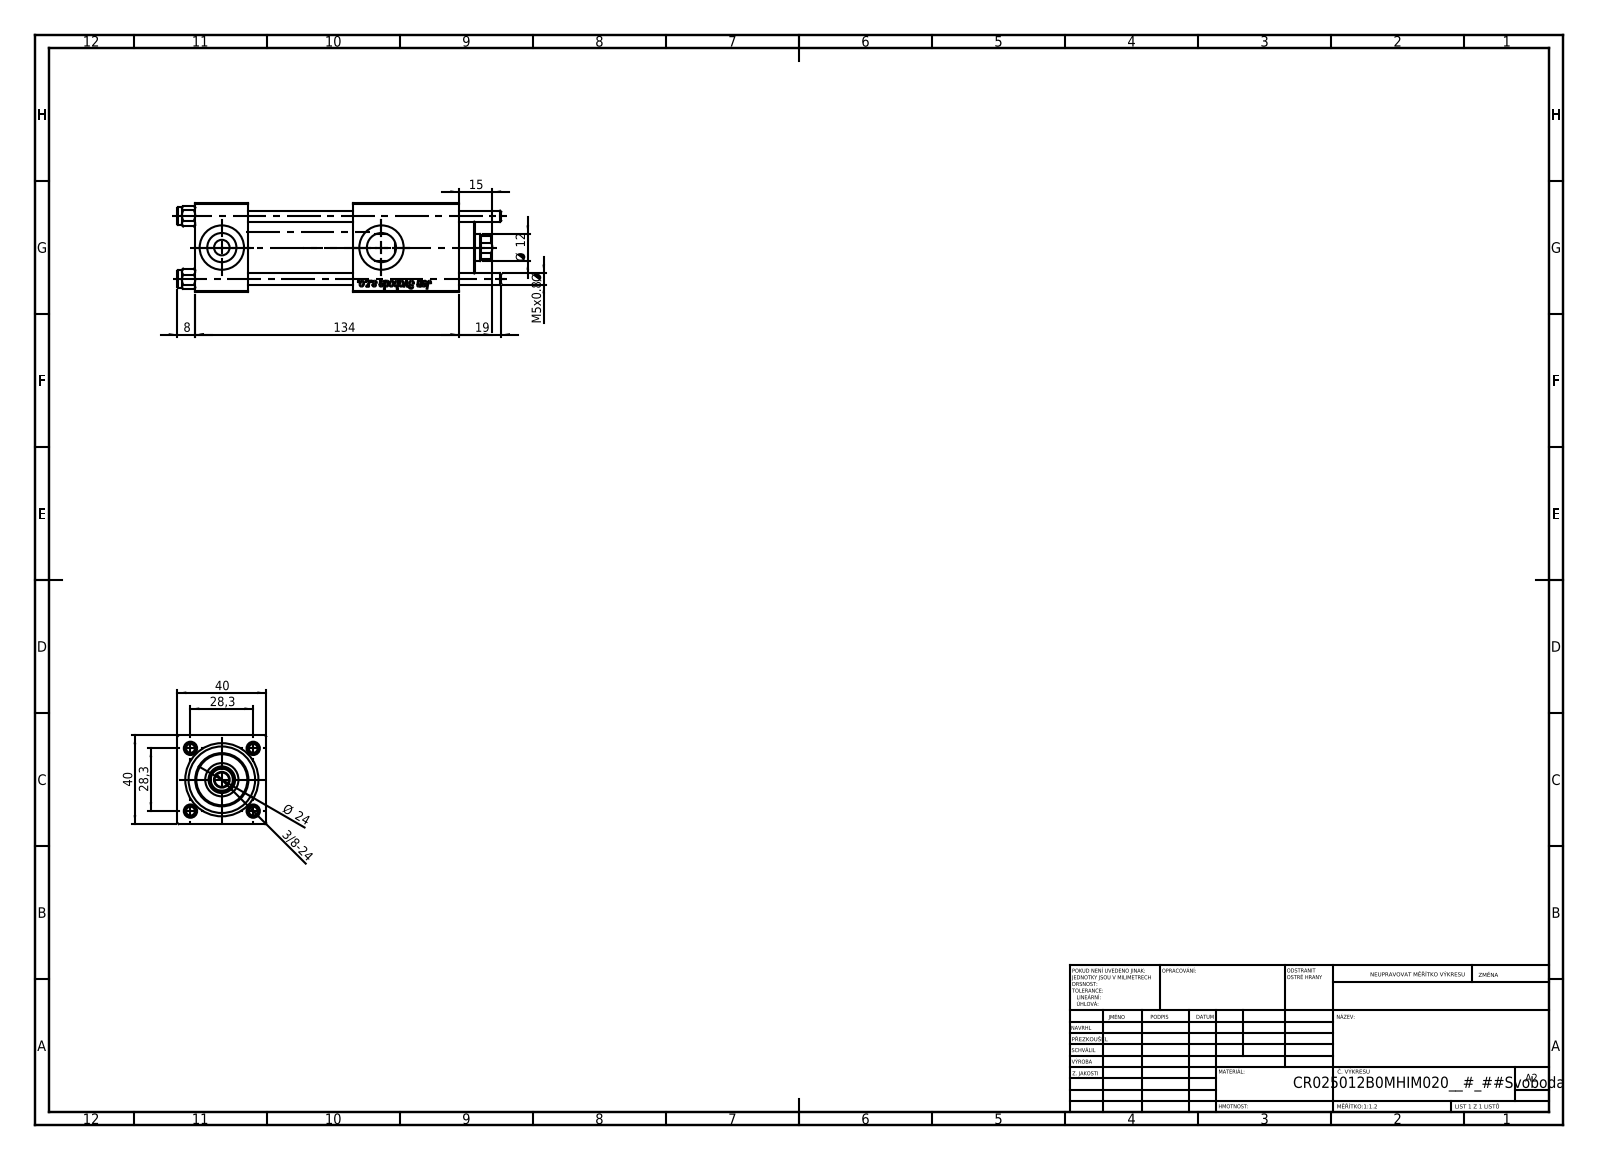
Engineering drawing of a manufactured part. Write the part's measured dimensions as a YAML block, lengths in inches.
part_name: "V215CR_VCP_B; V215_VC_A; NUT_M5_B; V215CR_B_TYCINKA (+1 more)"
step_written_by: "SolidWorks 2019 (CONFIG_CONTROL_DESIGN)"
units: inches
bodies: {solids: 11, faces: 1155, planar: 429, cylindrical: 78, other: 648}
overall_size: [5.748, 1.575, 1.575]
volume: 8.841
surface_area: 90.86
round_holes:
  - {diameter: 0.197, count: 4}
  - {diameter: 0.787, count: 3}
  - {diameter: 0.276, count: 2}
  - {diameter: 0.518, count: 2}
  - {diameter: 0.256, count: 1}
  - {diameter: 0.472, count: 1}
  - {diameter: 0.591, count: 1}
  - {diameter: 0.984, count: 1}
  - {diameter: 1.181, count: 1}
round_bosses_or_shafts:
  - {diameter: 0.315, count: 4}
  - {diameter: 1.22, count: 1}
  - {diameter: 0.945, count: 1}
partial_cylinders:
  - {radius: 0.217, count: 1}
face_to_face_distances: [1.575, 0.945, 3.555, 2.61, 2.795, 1.85, 0.76, 4.685, 3.74, 1.89]
hole_center_spacings: [0.788, 1.114, 1.576, 2.835]
